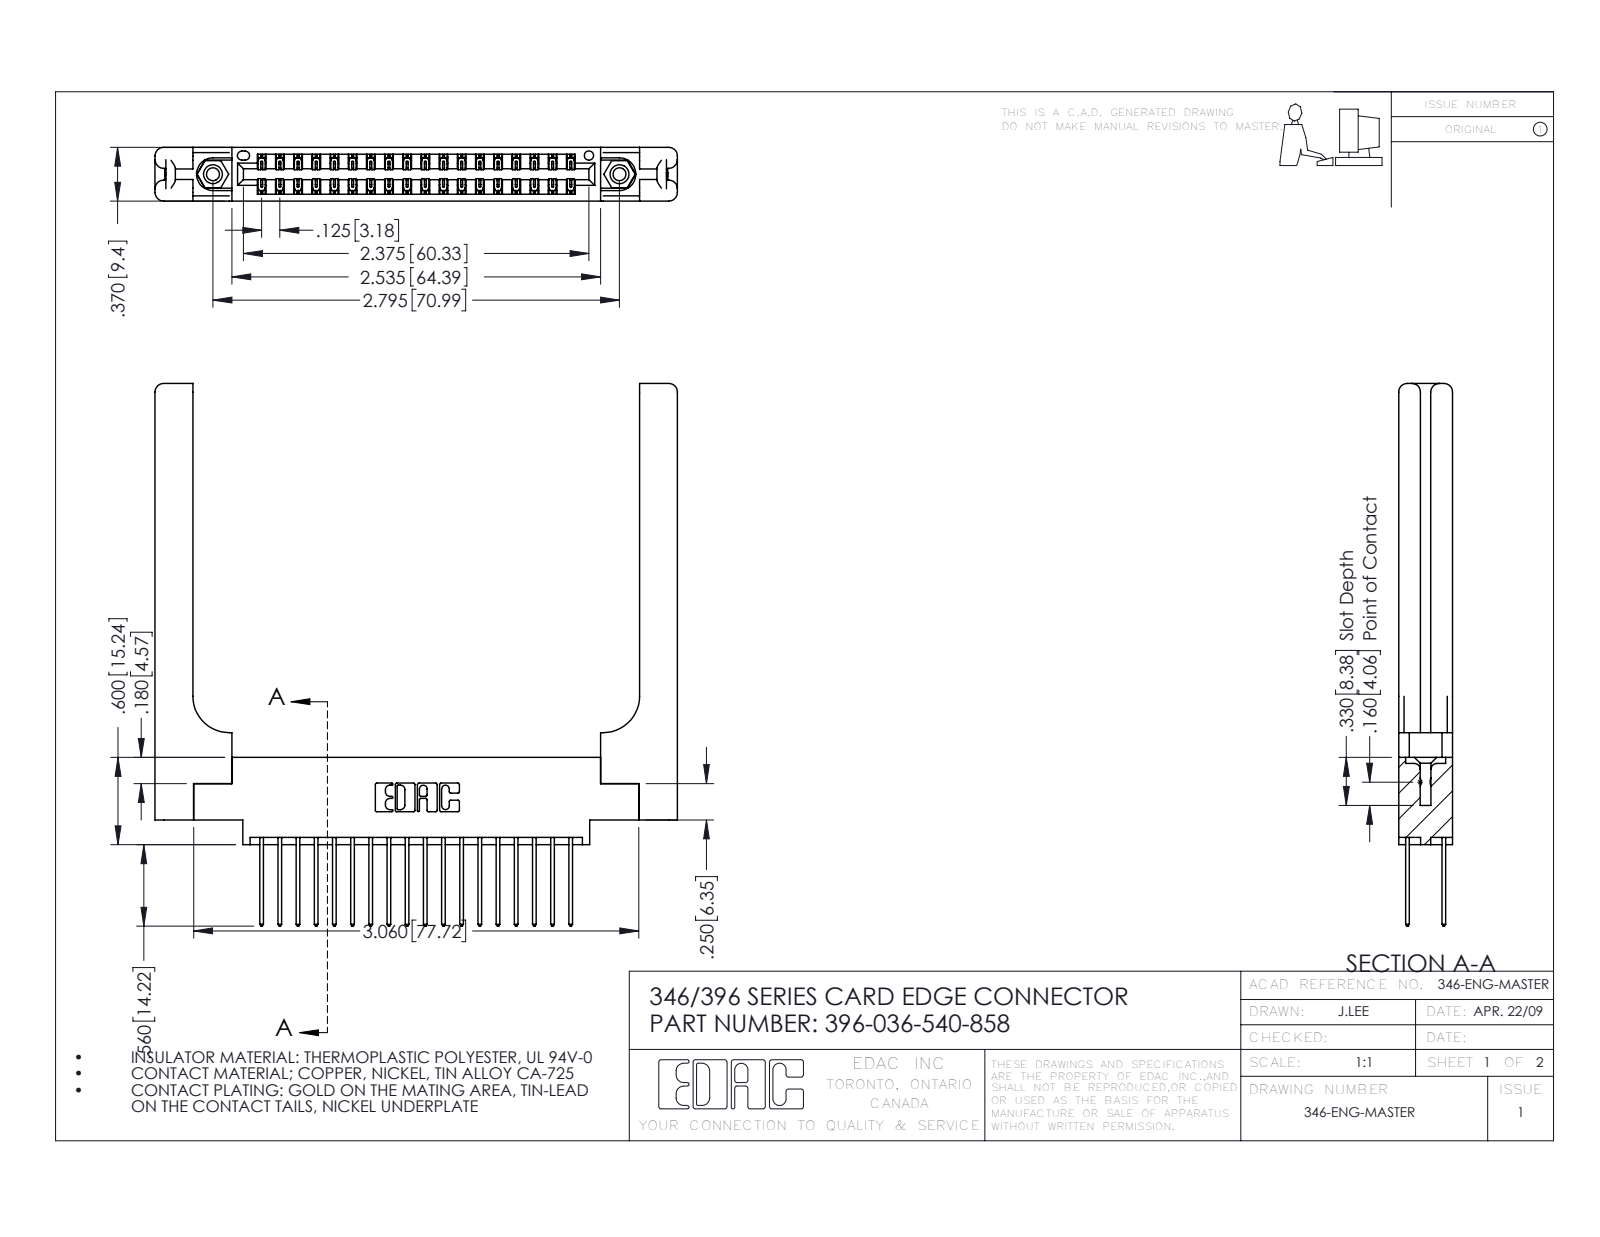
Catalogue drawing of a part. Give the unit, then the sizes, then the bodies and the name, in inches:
Units: inches
Overall size (bounding box): 3.73 × 3.591 × 0.37
Round holes (diameter × count): ⌀0.089 ×2, ⌀0.125 ×2, ⌀0.156 ×2, ⌀0.064 ×1
Round bosses / shafts (diameter × count): ⌀0.155 ×2
Partial cylindrical surfaces — rounded edges, fillets, slot ends (radius × count): R0.006 ×54, R0.01 ×36, R0.01 ×22, R0.06 ×16, R0.007 ×6, R0.031 ×6, R0.026 ×3, R0.014 ×2
Main face-to-face distances: 0.37, 0.072, 0.048, 0.322, 0.148, 0.15, 0.25, 0.025, 0.298, 0.077
Hole centre spacings: 0.246, 2.588, 2.795
Volume: 0.988 in³ · Surface area: 26.92 in²
Bodies: 41 solids, 2254 faces (1488 planar, 706 cylindrical, 60 other)
Part name (STEP PRODUCT): 346-220-058_345-220-058; 345-250-001_345-250-001-102; 345-292-001_345-293-140; 396-036-540-858 (+1 more)
STEP written by: SolidWorks 2016 (CONFIG_CONTROL_DESIGN)
